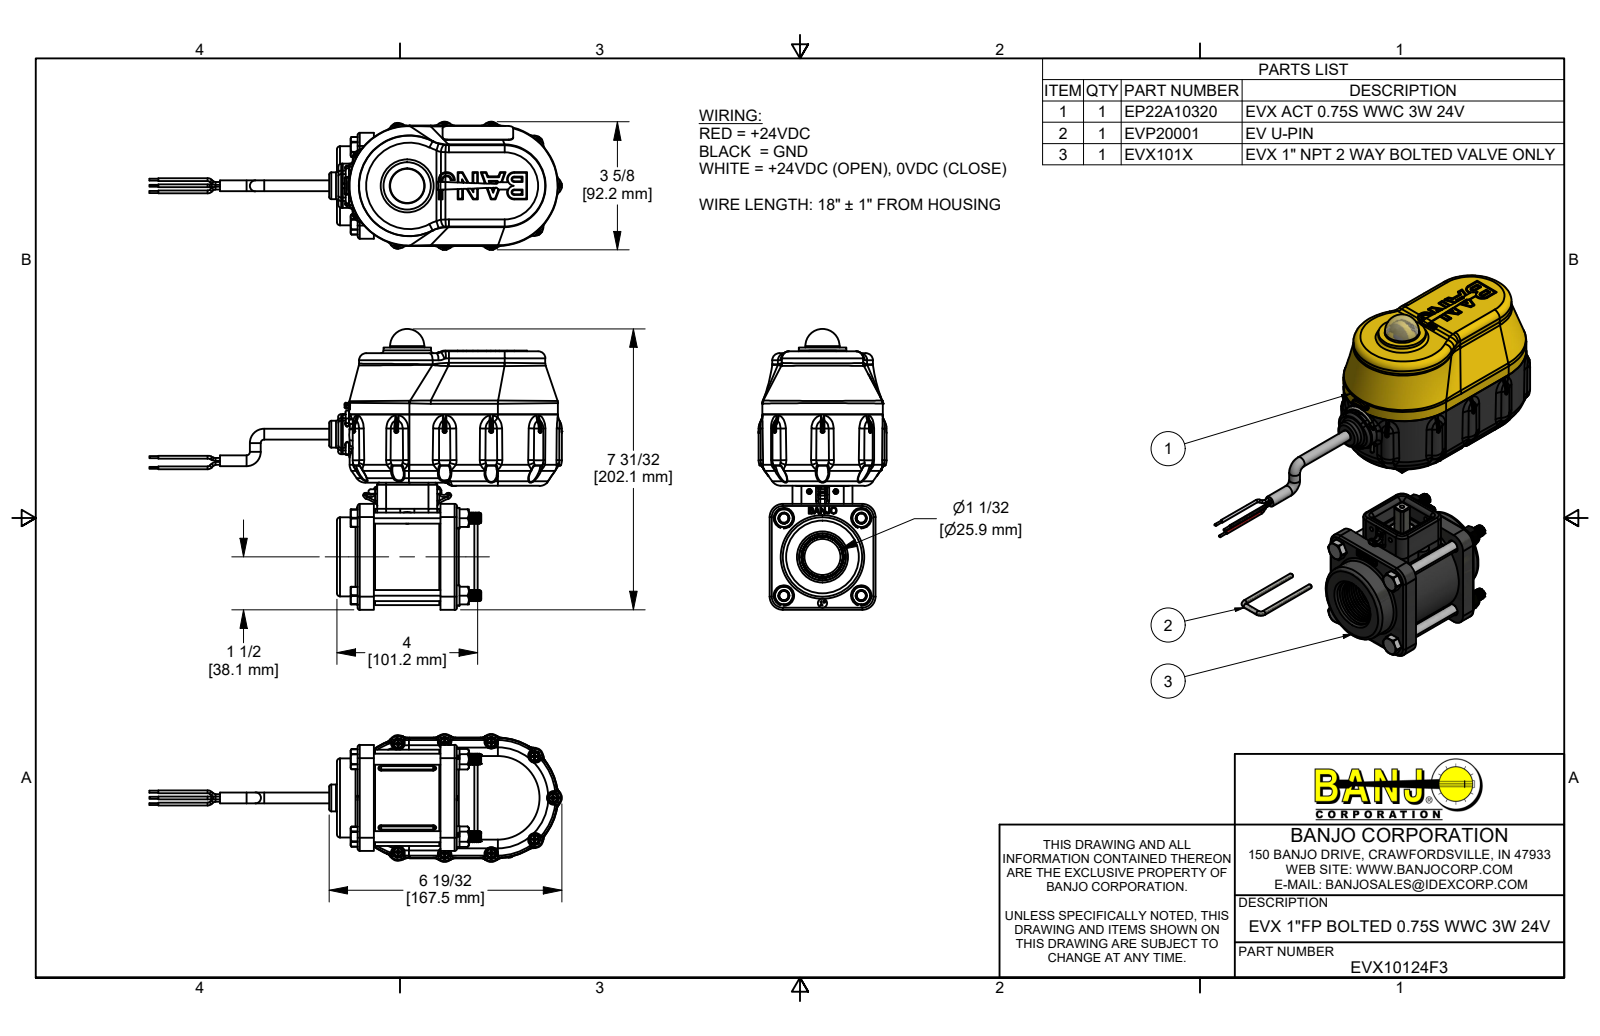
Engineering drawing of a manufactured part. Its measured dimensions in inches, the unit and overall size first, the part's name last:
Units: inches
Overall size (bounding box): 11.685 × 7.957 × 3.63
Round holes (diameter × count): ⌀0.095 ×11, ⌀0.15 ×11, ⌀0.08 ×7, ⌀0.107 ×4, ⌀0.126 ×4, ⌀0.136 ×4, ⌀0.148 ×4, ⌀0.15 ×4, ⌀0.17 ×4, ⌀0.252 ×4, ⌀0.322 ×4, ⌀1.02 ×3
Round bosses / shafts (diameter × count): ⌀0.268 ×60, ⌀0.25 ×17, ⌀0.08 ×15, ⌀0.14 ×11, ⌀0.108 ×11, ⌀0.085 ×11, ⌀0.058 ×6, ⌀0.313 ×5
Partial cylindrical surfaces — rounded edges, fillets, slot ends (radius × count): R0.013 ×180, R0.04 ×145, R0.01 ×84, R0.02 ×70, R0.06 ×58, R0.005 ×53, R0.03 ×38, R0.08 ×28
Main face-to-face distances: 0.1, 2.565, 0.46, 0.125, 0.211, 0.151, 0.06, 2.345, 0.055, 1.896
Hole centre spacings: 1.513, 2.192, 2.849, 3.789, 0.487, 0.668, 1.046, 1.117
Volume: 50.2 in³ · Surface area: 587.4 in²
Bodies: 96 solids, 11560 faces (2929 planar, 3483 cylindrical, 5148 other)
Part name (STEP PRODUCT): EVX10124; EP22A10320; B61905PPHS; B632038PM (+8 more)
STEP written by: Autodesk Inventor 2021 (AUTOMOTIVE_DESIGN)
